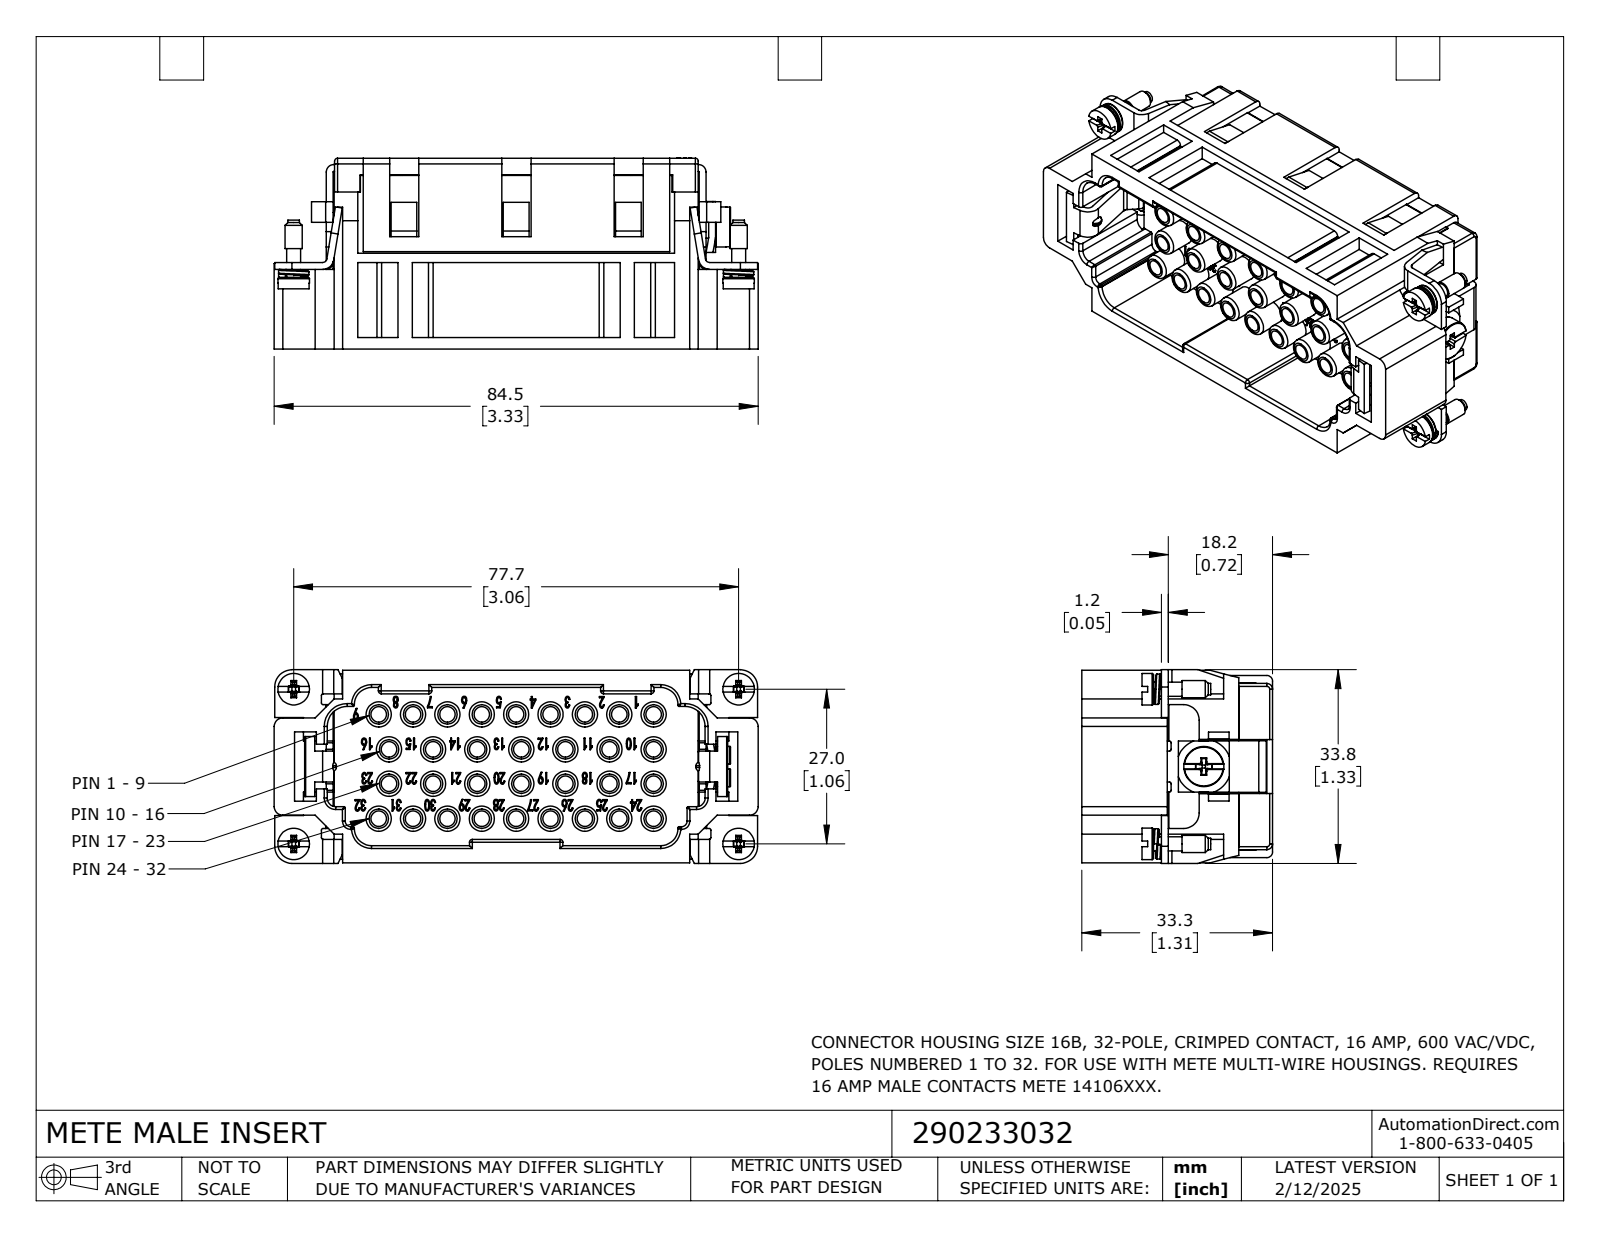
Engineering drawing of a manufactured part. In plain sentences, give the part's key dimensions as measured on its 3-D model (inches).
The part is named "290233032". Its 3-D file was written by "SolidWorks 2024 (CONFIG_CONTROL_DESIGN)". It is 14 solids with 3013 faces: 1583 planar, 761 cylindrical and 669 other. Overall it measures 3.327 by 1.331 by 1.311 inches. Its volume is 2.094 cubic inches and its surface area 69.65 square inches. Round holes: 35 of diameter 0.106, 32 of diameter 0.189, 12 of diameter 0.071, 4 of diameter 0.114, 1 of diameter 0.055, 1 of diameter 0.13. Round bosses or shafts: 32 of diameter 0.173, 12 of diameter 0.063, 4 of diameter 0.217, 4 of diameter 0.209, 4 of diameter 0.118, 4 of diameter 0.096, 4 of diameter 0.079, 3 of diameter 0.098. Partial cylindrical surfaces (rounded edges, fillets, slot ends): 64 of radius 0.165, 40 of radius 0.118, 38 of radius 0.059, 33 of radius 0.02, 32 of radius 0.01, 32 of radius 0.096, 12 of radius 0.004, 12 of radius 0.012. The main face-to-face distances are 0.028, 0.055, 1.197, 0.118, 1.169, 1.142, 0.063, 0.47, 1.224, 0.235. The hole center spacings are 0.236, 0.472, 0.303, 0.384, 0.754, 0.709, 0.858, 0.606.
